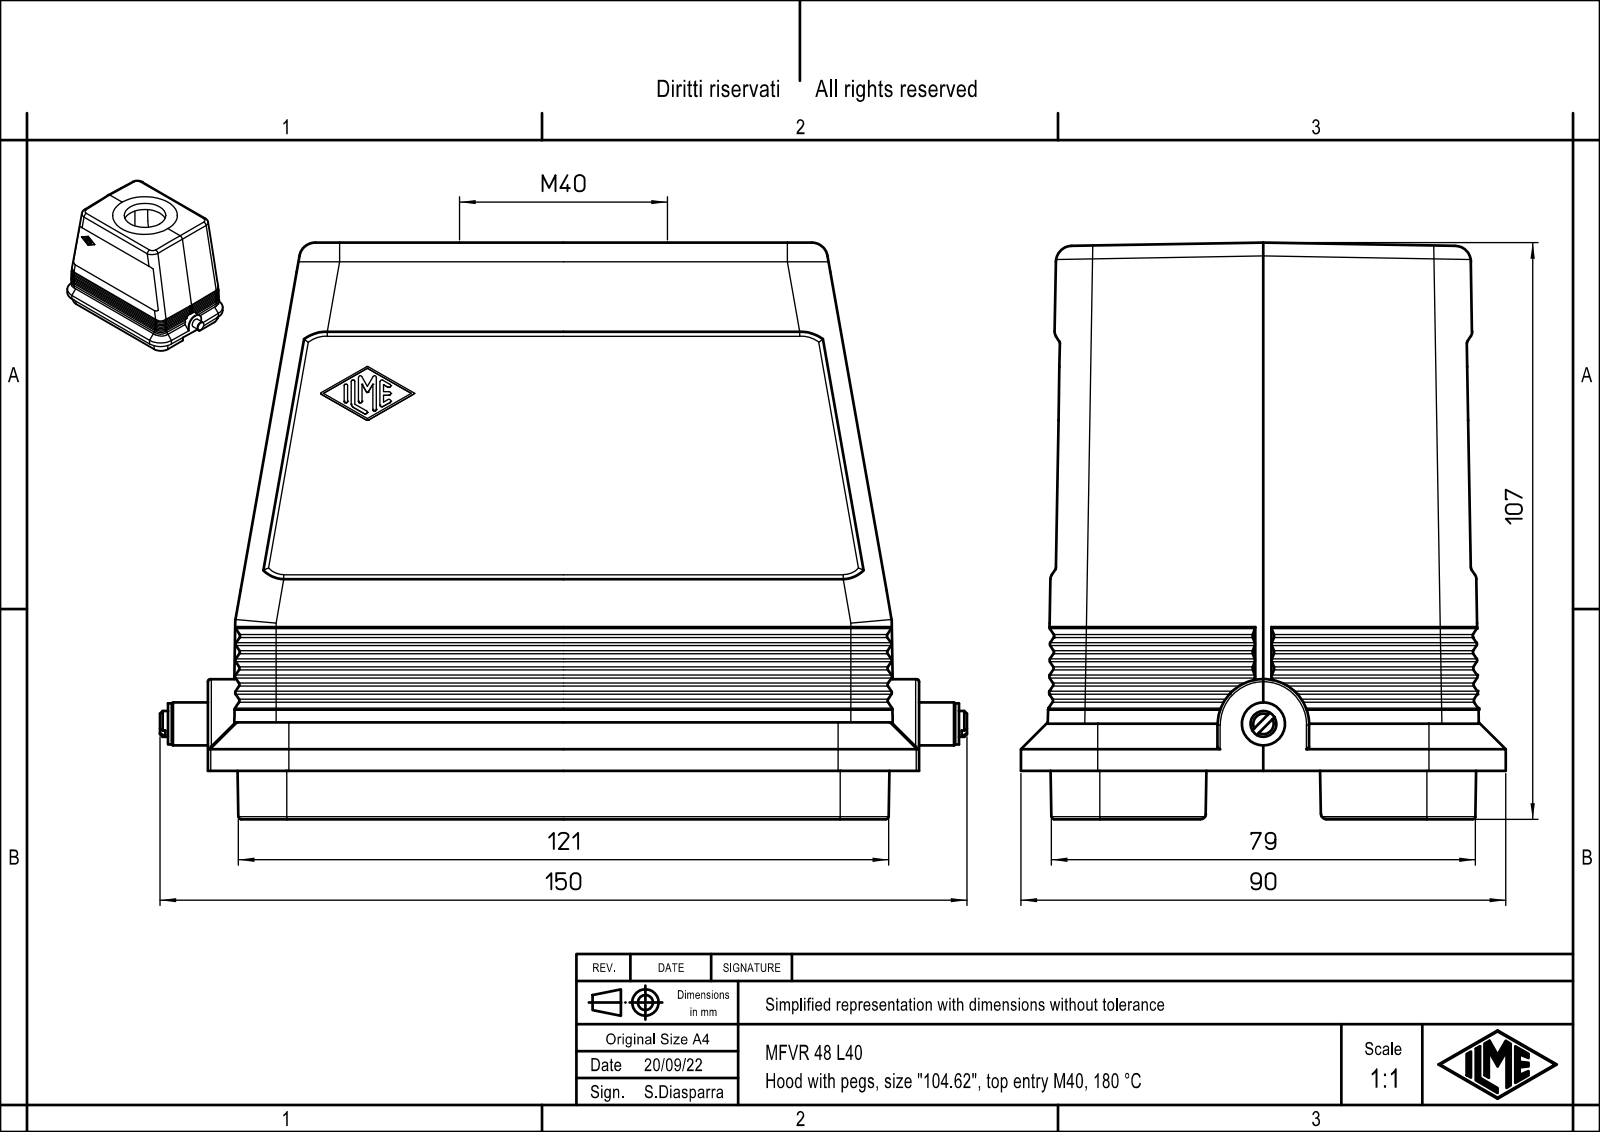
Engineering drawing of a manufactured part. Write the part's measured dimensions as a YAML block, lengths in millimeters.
part_name: "MFVR 48 L40"
step_written_by: "Creo Elements/Direct Modeling 20.1B 02-Apr-2019 (C) Parametric Technology GmbH (AUTOMOTIVE_DESIGN)"
units: millimeters
bodies: {solids: 1, faces: 728, planar: 242, cylindrical: 221, other: 265}
overall_size: [149.8, 107, 90]
volume: 202886
surface_area: 96298
round_holes:
  - {diameter: 3.5, count: 8}
  - {diameter: 38.6, count: 1}
round_bosses_or_shafts:
  - {diameter: 61, count: 1}
  - {diameter: 60, count: 1}
  - {diameter: 8, count: 1}
  - {diameter: 7.6, count: 1}
  - {diameter: 4.8, count: 1}
partial_cylinders:
  - {radius: 0.5, count: 85}
  - {radius: 7, count: 48}
  - {radius: 3, count: 11}
  - {radius: 1.5, count: 8}
  - {radius: 1, count: 5}
  - {radius: 4.5, count: 4}
  - {radius: 9, count: 4}
  - {radius: 14.5, count: 4}
face_to_face_distances: [0.99, 3.5, 7.95, 2.87, 94.5, 78.62, 79.61, 98, 91, 7]
hole_center_spacings: [27, 35, 52.15, 60.54, 104, 107.45, 109.73, 8]
